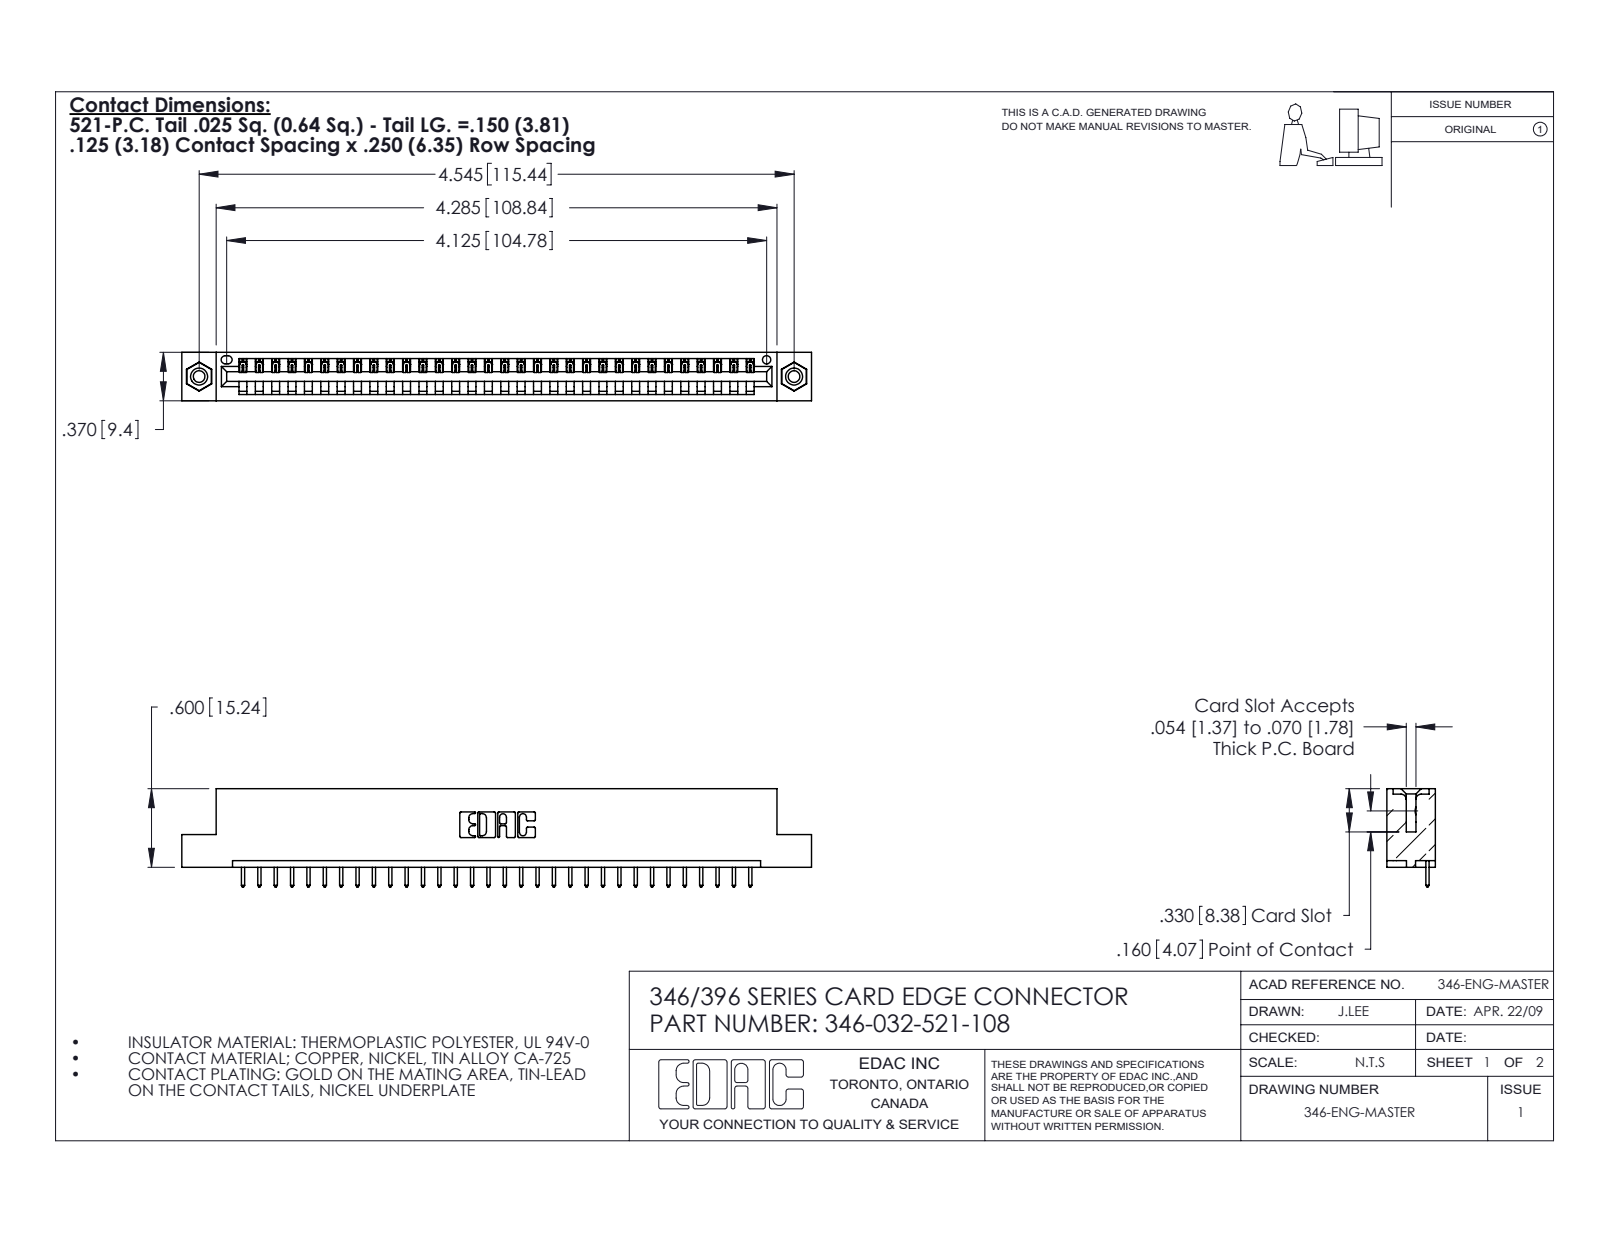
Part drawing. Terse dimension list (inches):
name: 345-292-001_345-293-121; 345-250-001_345-250-003-102; 346-032-521-108; 346 Part_Flush Mounting Lugs - 0.156 Dia-TI
written by: SolidWorks 2020 (CONFIG_CONTROL_DESIGN)
unit: in
bodies: 35 solids, 2038 faces (1388 planar, 634 cylindrical, 16 other)
size: 4.81 × 0.75 × 0.37
volume: 0.704 in³; area: 21.64 in²
holes: 2× ⌀0.089, 2× ⌀0.125, 2× ⌀0.156, 1× ⌀0.064
bosses: 2× ⌀0.155
rounds: 64× R0.006, 64× R0.01, 22× R0.01, 6× R0.007, 6× R0.031, 3× R0.026, 2× R0.031, 2× R0.04
face distances: 0.048, 0.322, 0.37, 0.25, 0.072, 0.298, 0.025, 0.148, 0.222, 0.1
hole spacings: 0.246, 4.337, 4.545
